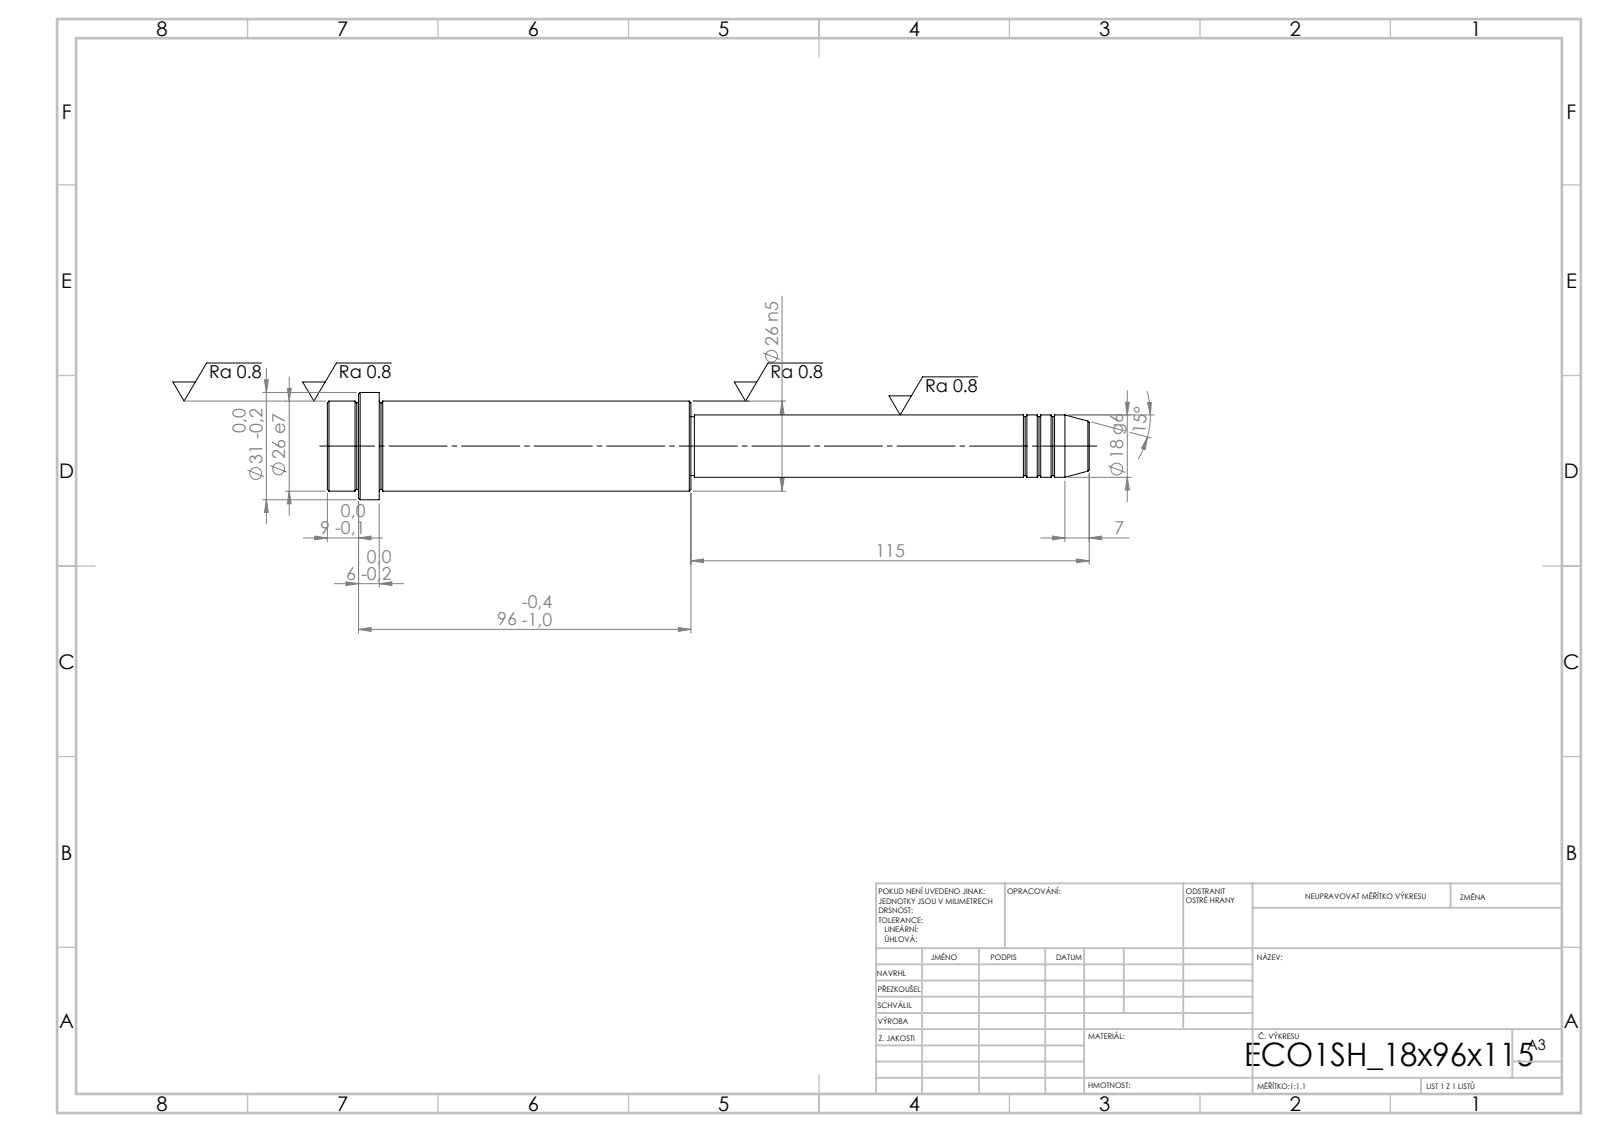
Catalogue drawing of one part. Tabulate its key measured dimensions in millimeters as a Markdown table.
| quantity | value |
| --- | --- |
| STEP written by | SolidWorks 2019 (CONFIG_CONTROL_DESIGN) |
| units | millimeters |
| bodies | 1 solid, 52 faces (6 planar, 16 cylindrical, 30 other) |
| overall size | 220 × 31 × 31 |
| volume | 85 820 mm³ |
| surface area | 16 703 mm² |
| round bosses / shafts (diameter × count) | 31 × 1, 26 × 1, 18 × 1, 17 × 1 |
| main face-to-face distances | 105, 90, 15, 96, 6, 9, 115, 205, 211, 220 |
